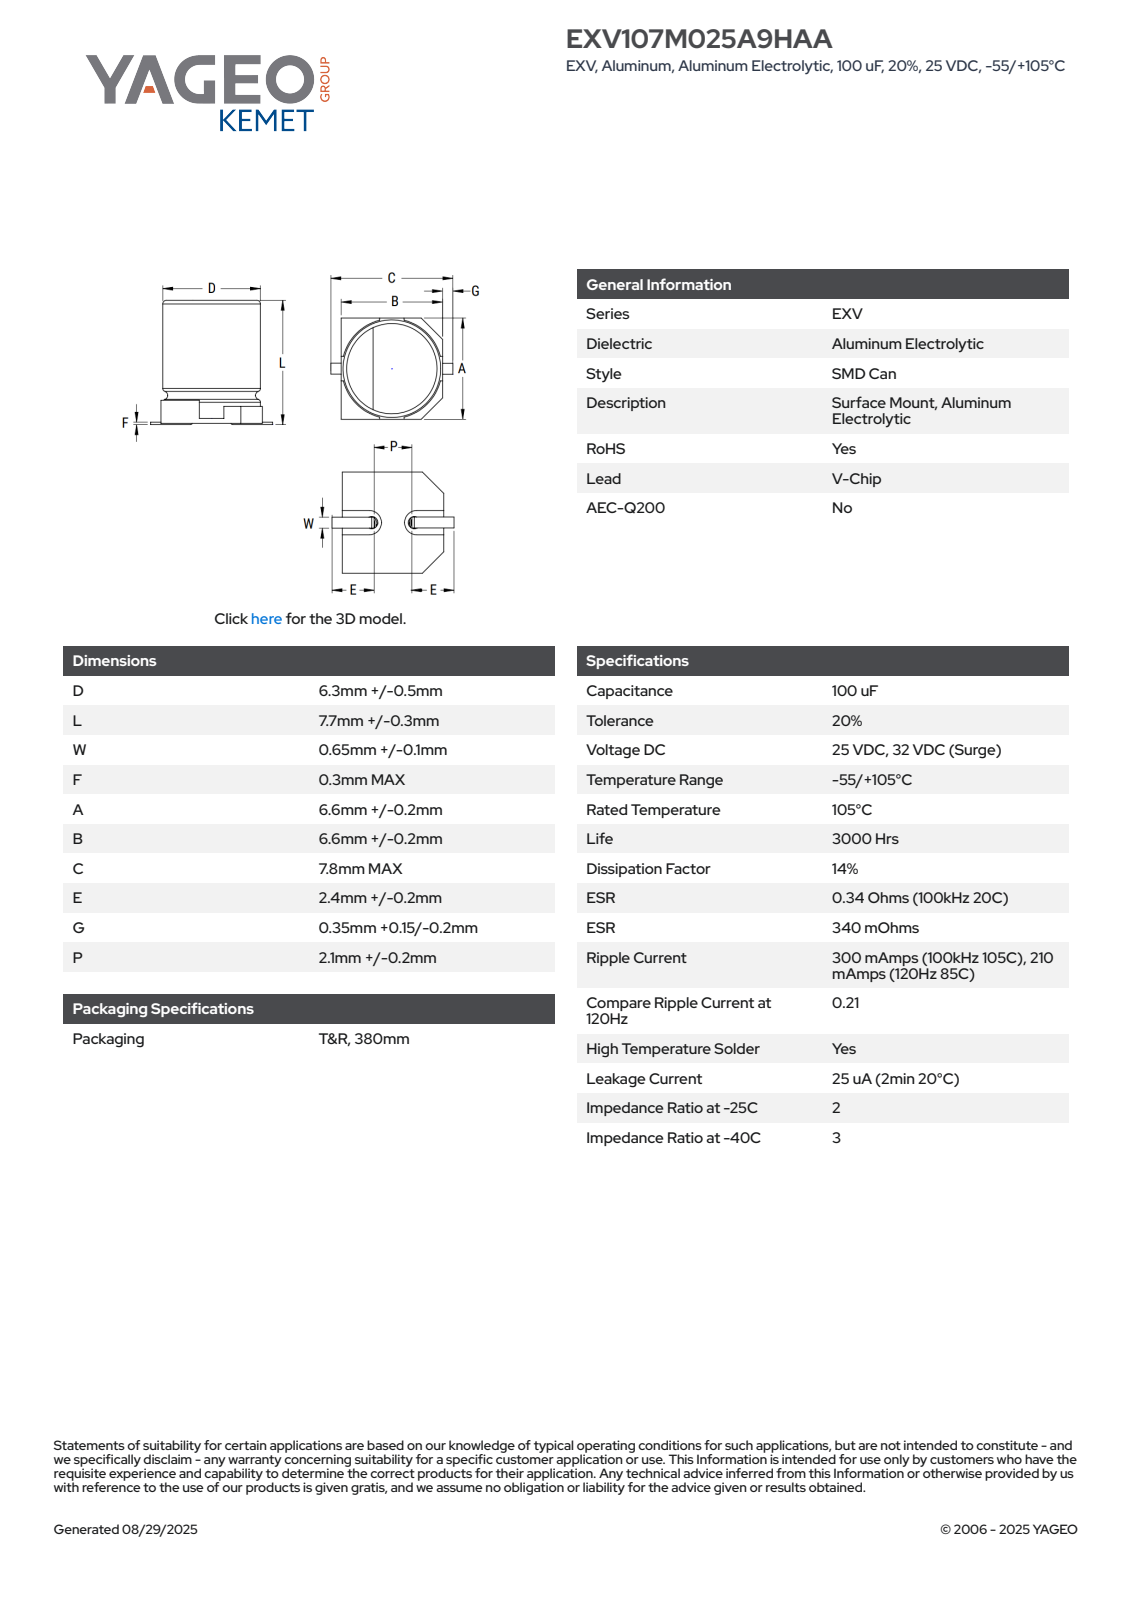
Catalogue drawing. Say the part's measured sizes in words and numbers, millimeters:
The part is named "CAC_S_6.3X7.7_D6.8L8W0.75F0.3A6.8B6.8C7.8E2.8P2". Its 3-D file was written by "SolidWorks 2014 (AUTOMOTIVE_DESIGN)". It is 5 solids with 78 faces: 61 planar, 11 cylindrical and 6 other. Overall it measures 8.01 by 7.6 by 6.8 millimeters. Its volume is 266 cubic millimeters and its surface area 359 square millimeters. Round bosses or shafts: 1 of diameter 6.5. Partial cylindrical surfaces (rounded edges, fillets, slot ends): 2 of radius 0.2, 1 of radius 2.7, 1 of radius 3.4. The main face-to-face distances are 0.4, 7.7, 7.3, 7.71, 7.31, 6.8, 2, 1.6, 5.7, 5.71.
